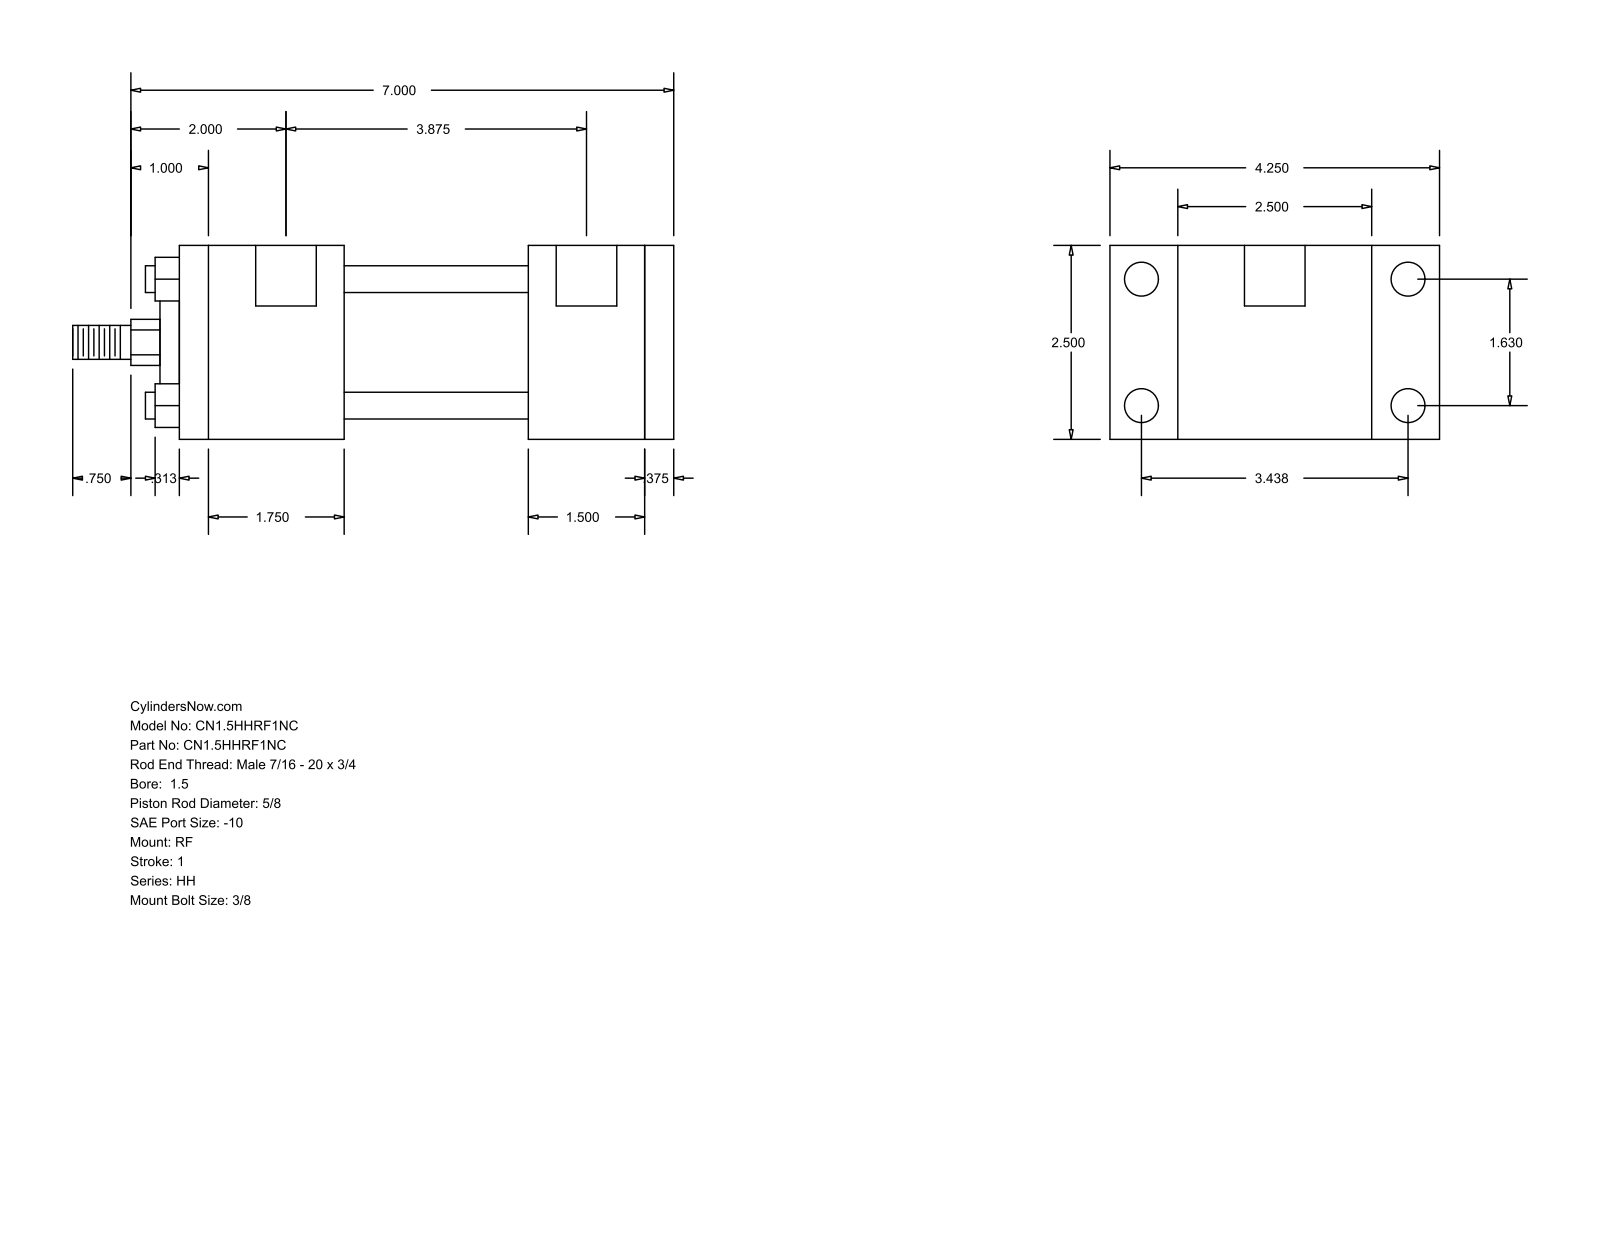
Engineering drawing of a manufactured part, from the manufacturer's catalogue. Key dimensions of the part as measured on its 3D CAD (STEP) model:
Part name (STEP PRODUCT): HH_RF__0150_0.625
STEP written by: GSSL Pune (CONFIG_CONTROL_DESIGN)
Units: millimetres
Bodies: 0 solids, 92 faces (64 planar, 28 cylindrical, 0 other)
Overall size (bounding box): 196.85 × 107.95 × 63.5
Round holes (diameter × count): ⌀5.56 ×4, ⌀11.13 ×4, ⌀19.84 ×2
Round bosses / shafts (diameter × count): ⌀8.76 ×4, ⌀44.45 ×1, ⌀28.57 ×1, ⌀15.88 ×1, ⌀11.11 ×1
Partial cylindrical surfaces — rounded edges, fillets, slot ends (radius × count): R7.54 ×1
Main face-to-face distances: 63.5, 161.92, 38.1, 152.4, 9.52, 60.33, 53.97, 114.3, 98.43, 107.95
Hole centre spacings: 1.59, 41.4, 87.32, 96.64, 100.01, 101.6, 98.42
